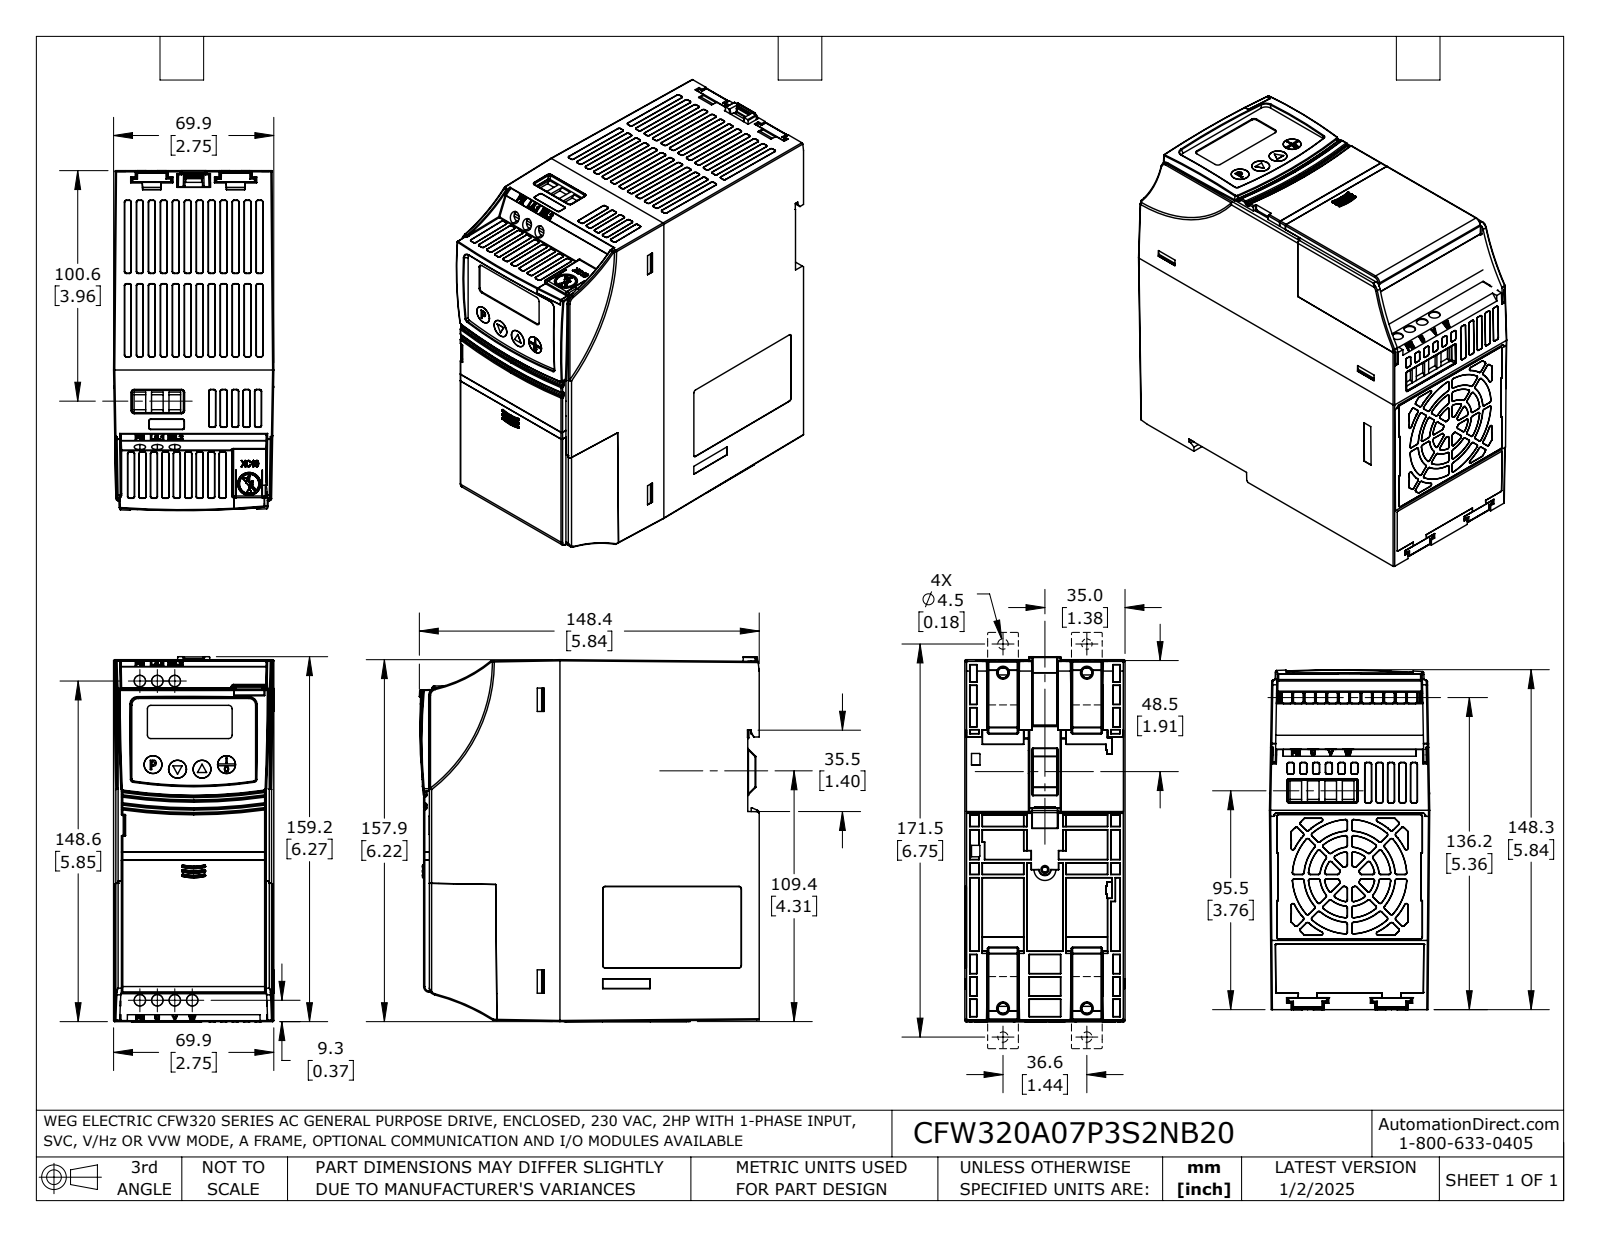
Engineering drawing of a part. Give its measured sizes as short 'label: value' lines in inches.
name: CFW320A07P3S2NB20
written by: SolidWorks 2021 (AUTOMOTIVE_DESIGN)
unit: in
bodies: 6 solids, 3715 faces (1587 planar, 853 cylindrical, 1275 other)
size: 6.269 × 5.841 × 2.754
volume: 15.24 in³; area: 309 in²
holes: 3× ⌀0.197
rounds: 327× R0.012, 150× R0.02, 13× R0.039, 5× R0.03, 3× R0.118, 2× R0.01, 1× R0.098, 1× R0.126
face distances: 0.07, 0.055, 0.019, 0.05, 6, 5.33, 5.275, 5.571, 5.516, 0.241
hole spacings: 0.3, 0.6
